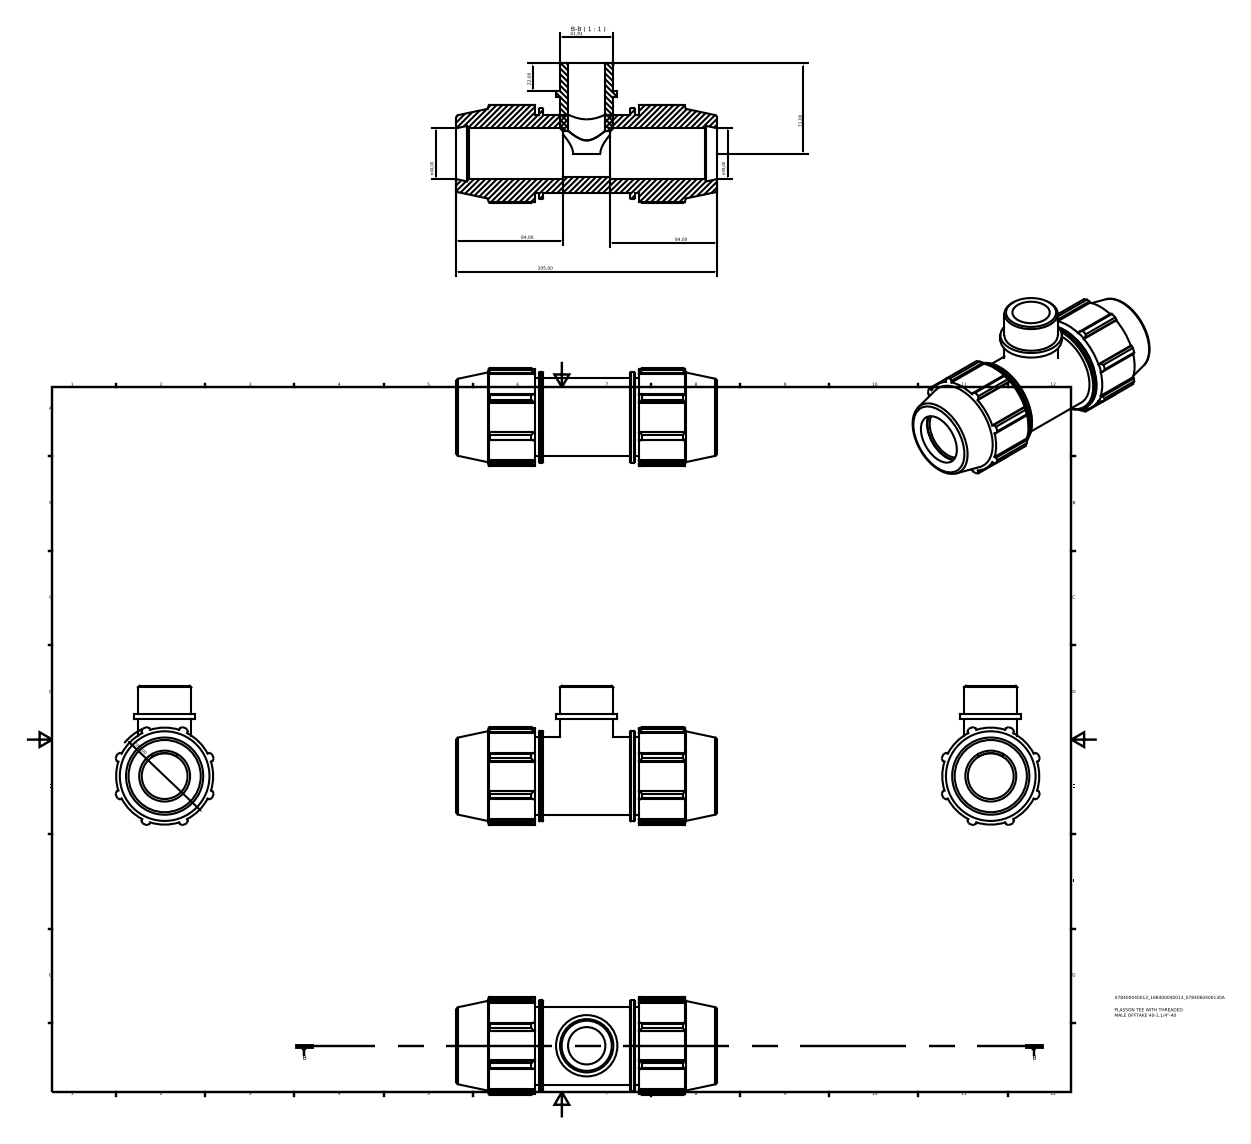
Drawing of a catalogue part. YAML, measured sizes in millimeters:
part_name: "078400040013_188400040013"
step_written_by: "Autodesk Inventor 2015 (AUTOMOTIVE_DESIGN)"
units: millimeters
bodies: {solids: 2, faces: 162, planar: 83, cylindrical: 48, other: 31}
overall_size: [205, 109.58, 77.16]
volume: 544477
surface_area: 99904
round_holes:
  - {diameter: 29.34, count: 1}
  - {diameter: 36, count: 1}
  - {diameter: 40, count: 1}
round_bosses_or_shafts:
  - {diameter: 71.34, count: 1}
  - {diameter: 61.5, count: 1}
  - {diameter: 48.2, count: 1}
  - {diameter: 41.91, count: 1}
partial_cylinders:
  - {radius: 38.13, count: 1}
  - {radius: 41, count: 1}
face_to_face_distances: [61.5, 143.5, 64.92, 68.33, 136.67, 140.08, 3.42, 6.83, 75.17, 78.58]
